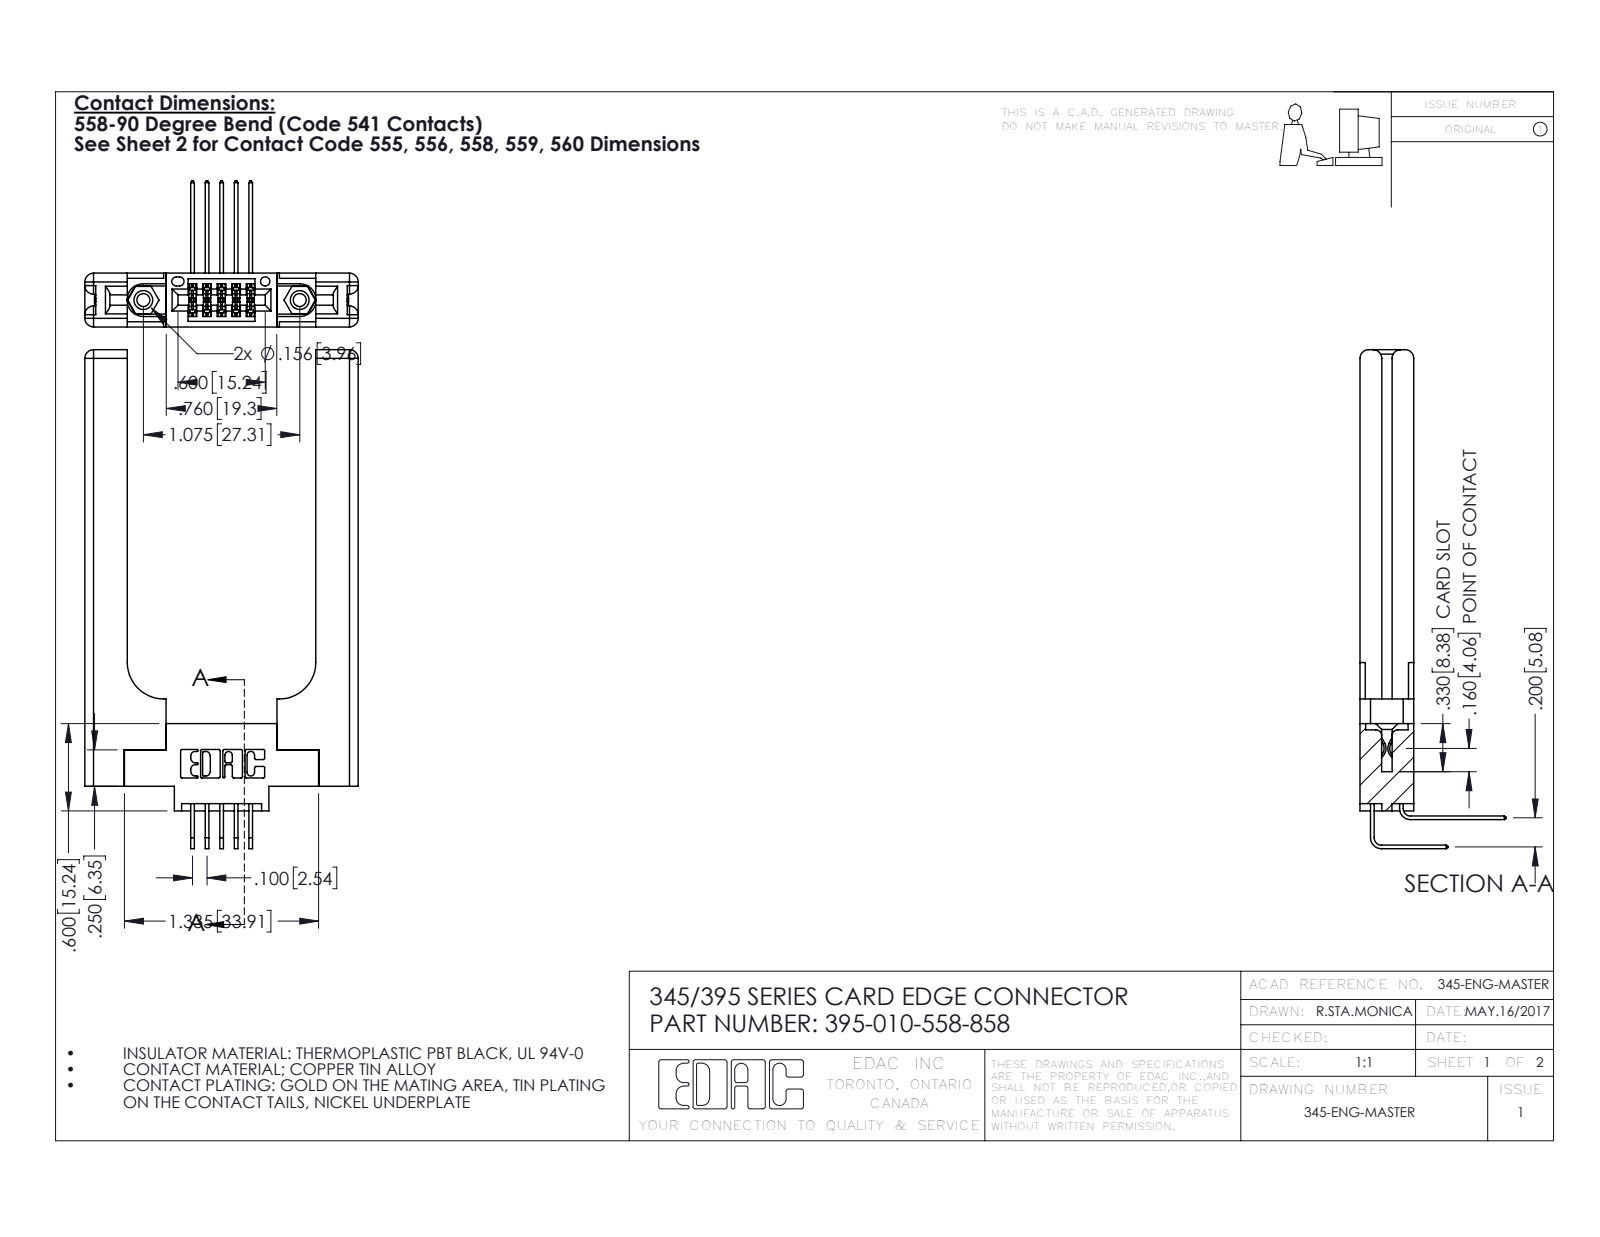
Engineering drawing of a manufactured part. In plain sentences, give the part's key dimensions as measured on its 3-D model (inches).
The part is named "345-220-058_345-220-058; 345-292-001_558 559 Tail - 1; 395-010-558-858; 345 Part_0.170 Offset - 0.156 Dia-TH (+2 more)". Its 3-D file was written by "SolidWorks 2016 (CONFIG_CONTROL_DESIGN)". It is 15 solids with 906 faces: 582 planar, 264 cylindrical and 60 other. Overall it measures 3.429 by 1.879 by 1.005 inches. Its volume is 0.776 cubic inches and its surface area 17.08 square inches. Round holes: 2 of diameter 0.089, 2 of diameter 0.125, 2 of diameter 0.156, 1 of diameter 0.064. Round bosses or shafts: 2 of diameter 0.155. Partial cylindrical surfaces (rounded edges, fillets, slot ends): 22 of radius 0.01, 16 of radius 0.006, 16 of radius 0.06, 6 of radius 0.007, 6 of radius 0.031, 3 of radius 0.026, 2 of radius 0.014, 2 of radius 0.019. The main face-to-face distances are 0.37, 0.15, 0.22, 0.072, 1.296, 0.148, 0.077, 0.298, 0.071, 0.292. The hole center spacings are 0.27, 0.847, 1.075.
